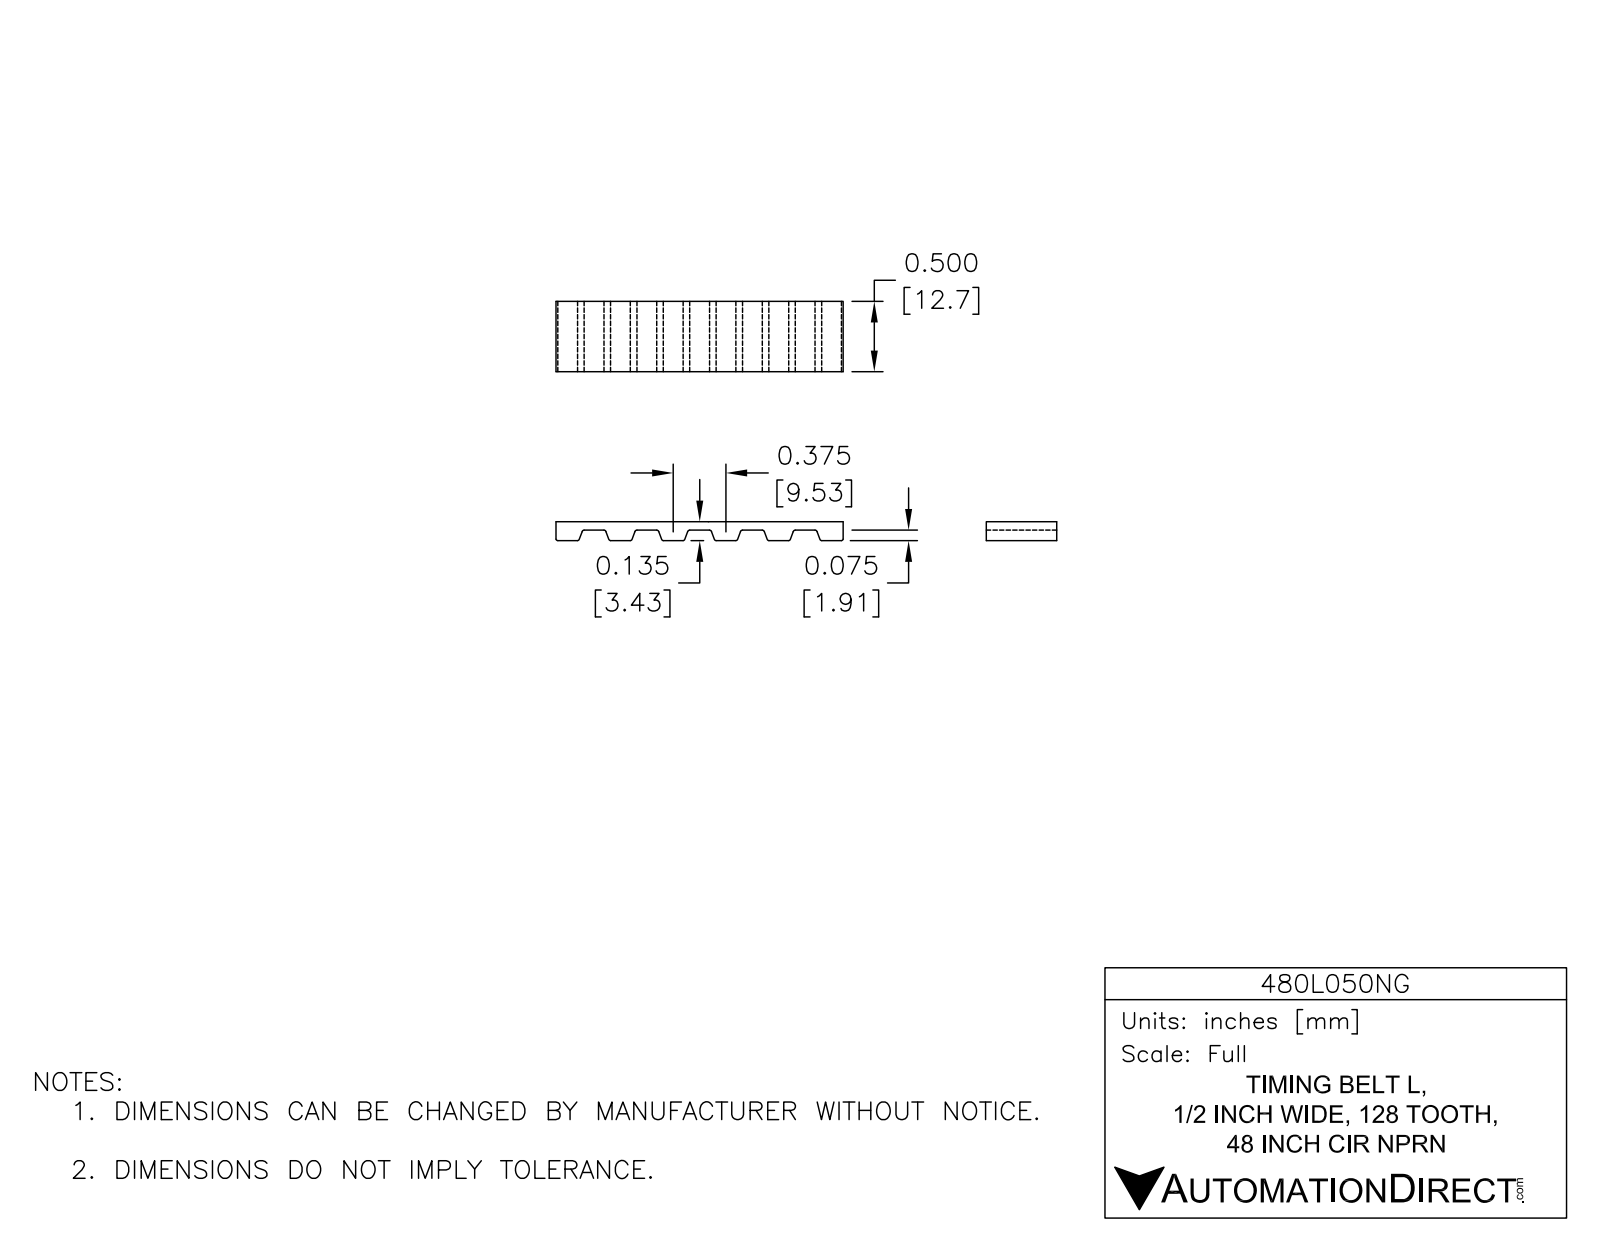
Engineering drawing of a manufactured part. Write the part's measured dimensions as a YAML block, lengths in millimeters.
part_name: "480L050NG"
step_written_by: "SolidWorks 2014 (AUTOMOTIVE_DESIGN)"
units: millimeters
bodies: {solids: 1, faces: 1040, planar: 489, cylindrical: 551, other: 0}
overall_size: [566.1, 76.2, 12.7]
volume: 35710
surface_area: 40170
partial_cylinders:
  - {radius: 0.5, count: 508}
  - {radius: 36.4, count: 2}
  - {radius: 38.1, count: 2}
face_to_face_distances: [1.7, 74.5, 76.2, 72.9, 12.7, 3.6, 72.6, 1.9, 71, 69.1]
